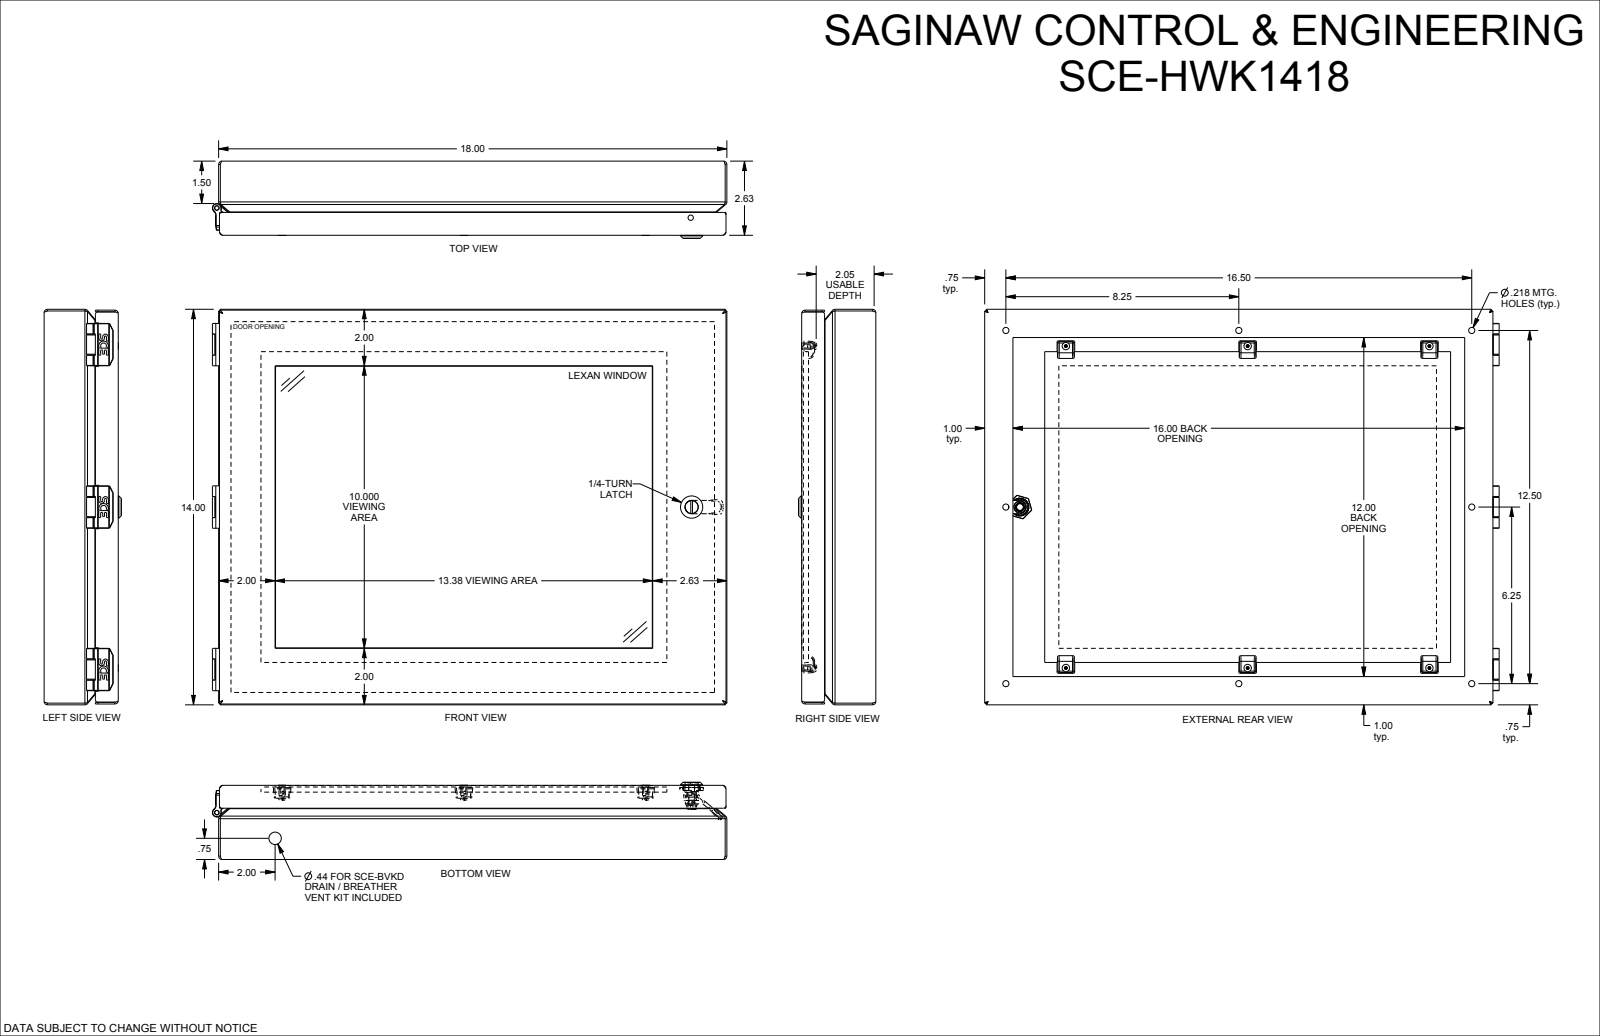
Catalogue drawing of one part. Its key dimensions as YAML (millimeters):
part_name: "SCE-HWK1418"
step_written_by: "SolidWorks 2021 (AUTOMOTIVE_DESIGN)"
units: millimeters
bodies: {solids: 49, faces: 1950, planar: 772, cylindrical: 495, other: 683}
overall_size: [462.8, 355.6, 69.4]
volume: 1055000
surface_area: 780000
round_holes:
  - {diameter: 3.5, count: 6}
  - {diameter: 4, count: 6}
  - {diameter: 4.1, count: 6}
  - {diameter: 5.4, count: 6}
  - {diameter: 7.2, count: 6}
  - {diameter: 0.5, count: 3}
  - {diameter: 2.5, count: 3}
  - {diameter: 6.8, count: 3}
  - {diameter: 4, count: 1}
  - {diameter: 4.8, count: 1}
  - {diameter: 5.1, count: 1}
  - {diameter: 6.1, count: 1}
round_bosses_or_shafts:
  - {diameter: 12.3, count: 6}
  - {diameter: 6.7, count: 6}
  - {diameter: 6, count: 6}
  - {diameter: 5.4, count: 6}
  - {diameter: 4.1, count: 6}
  - {diameter: 6.6, count: 3}
  - {diameter: 4.6, count: 3}
  - {diameter: 20, count: 1}
partial_cylinders:
  - {radius: 0.8, count: 40}
  - {radius: 0.2, count: 36}
  - {radius: 1.3, count: 36}
  - {radius: 0.3, count: 31}
  - {radius: 0.3, count: 16}
  - {radius: 0.5, count: 13}
  - {radius: 1.6, count: 10}
  - {radius: 0.6, count: 7}
face_to_face_distances: [1.5, 4.6, 6, 1.4, 1.5, 6.1, 60.6, 65.2, 66.5, 66.7]
hole_center_spacings: [146.1, 292.1, 209.6, 380.4, 0.4, 289.4, 317.5, 16.1]
